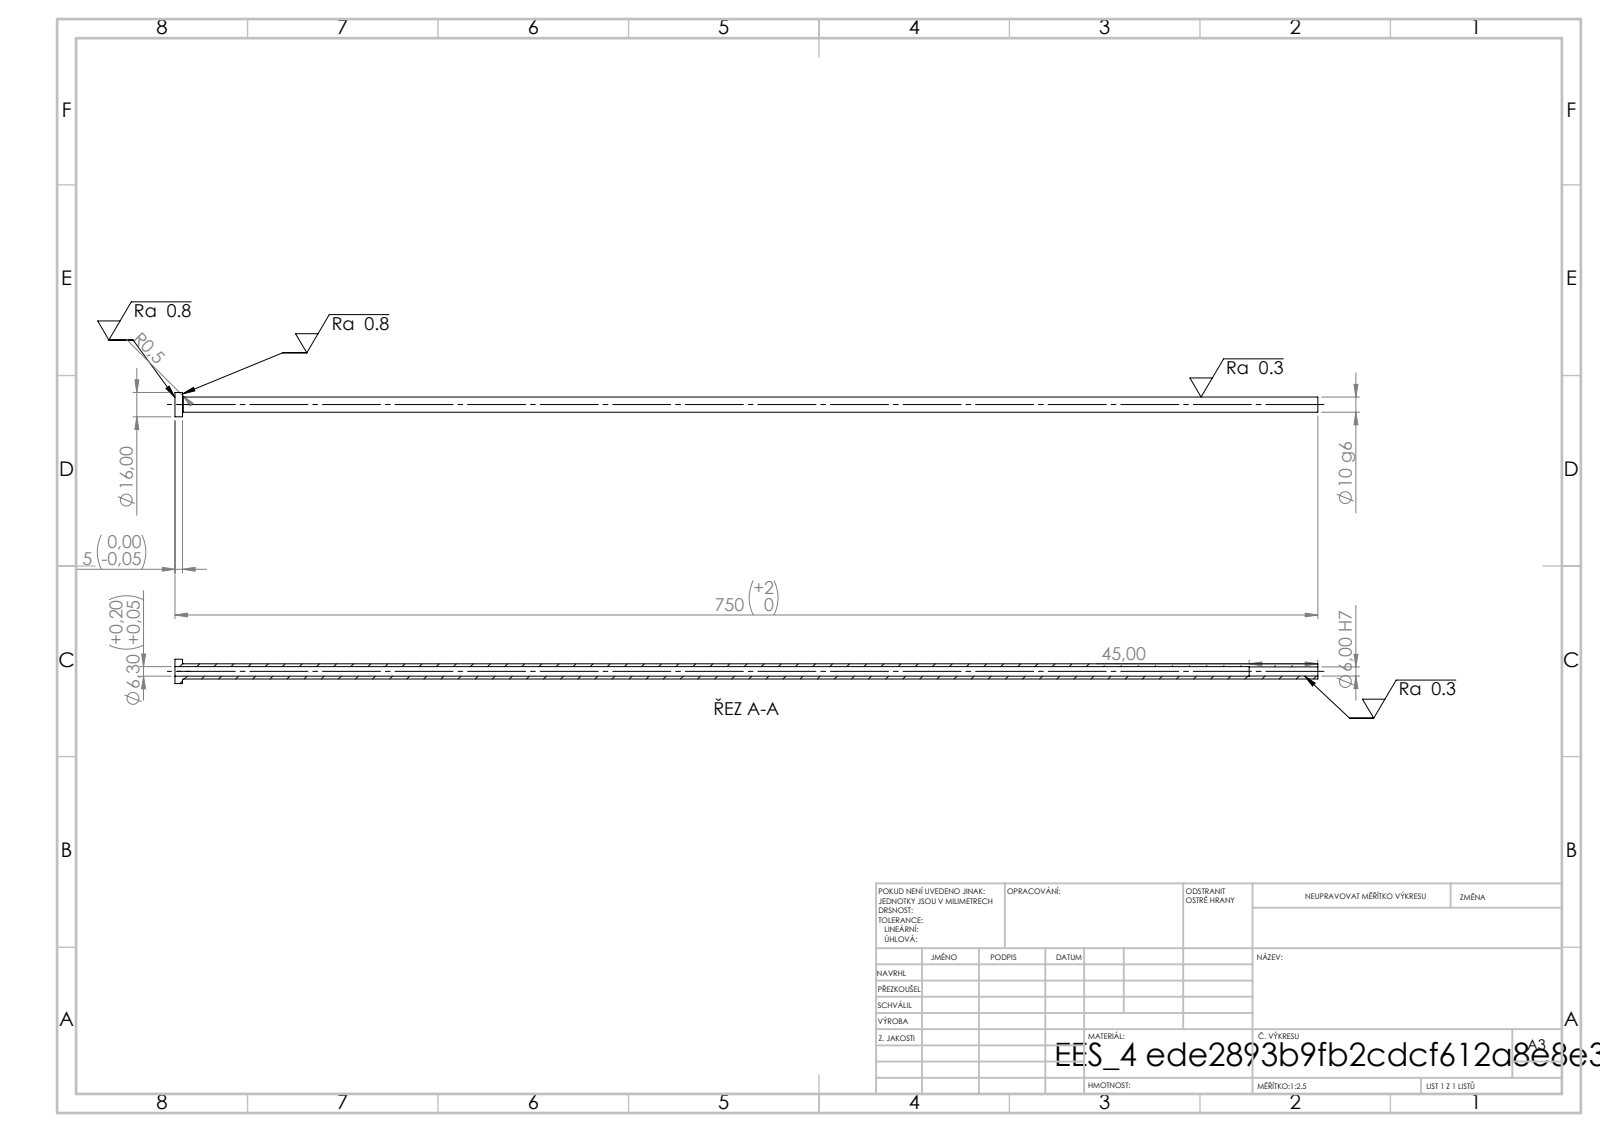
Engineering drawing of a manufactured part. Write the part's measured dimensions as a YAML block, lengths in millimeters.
step_written_by: "SolidWorks 2019 (CONFIG_CONTROL_DESIGN)"
units: millimeters
bodies: {solids: 1, faces: 14, planar: 4, cylindrical: 8, other: 2}
overall_size: [750, 16, 16]
volume: 36270
surface_area: 38797
round_holes:
  - {diameter: 6, count: 1}
  - {diameter: 6.3, count: 1}
round_bosses_or_shafts:
  - {diameter: 16, count: 1}
  - {diameter: 10, count: 1}
face_to_face_distances: [5, 750, 745, 705, 700, 45]
